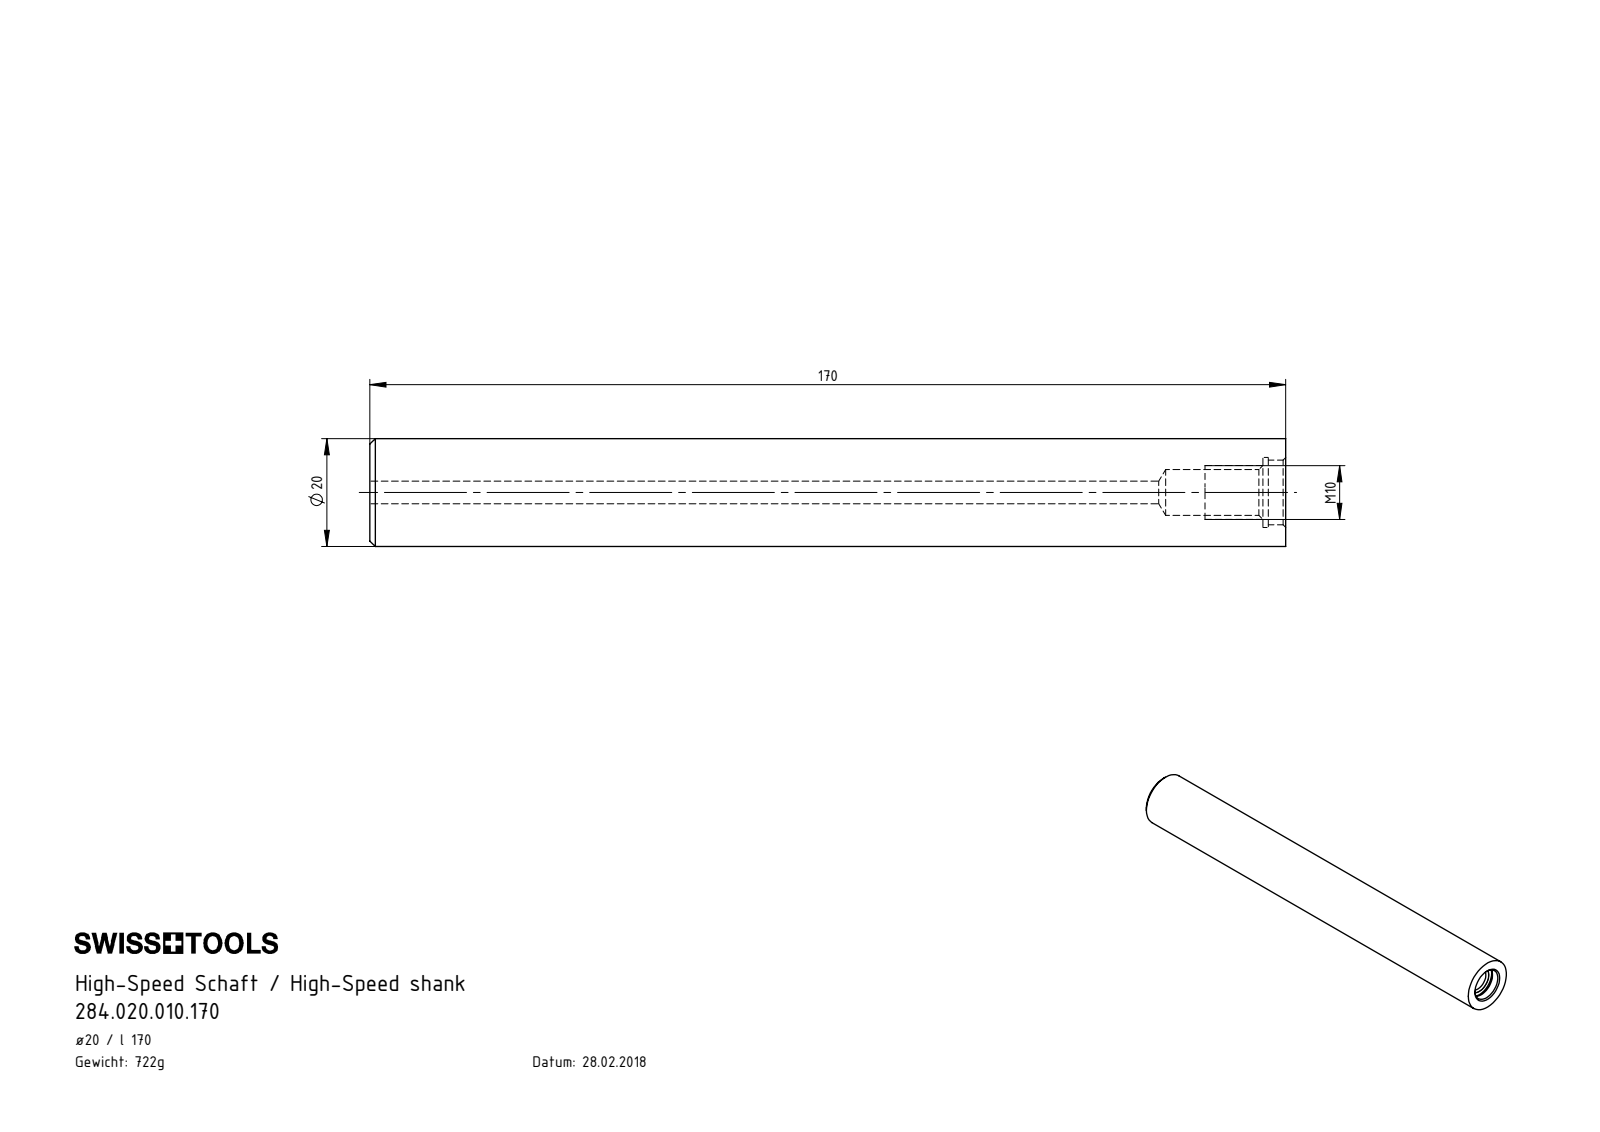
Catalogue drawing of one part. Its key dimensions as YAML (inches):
part_name: "284.020.010.170"
step_written_by: "SolidWorks 2017 (CONFIG_CONTROL_DESIGN)"
units: inches
bodies: {solids: 1, faces: 22, planar: 4, cylindrical: 10, other: 8}
overall_size: [6.693, 0.787, 0.787]
volume: 3.037
surface_area: 21.46
round_holes:
  - {diameter: 0.165, count: 1}
  - {diameter: 0.335, count: 1}
  - {diameter: 0.472, count: 1}
  - {diameter: 0.512, count: 1}
round_bosses_or_shafts:
  - {diameter: 0.787, count: 1}
face_to_face_distances: [6.693, 6.526, 0.167, 6.565, 0.039, 0.128]
